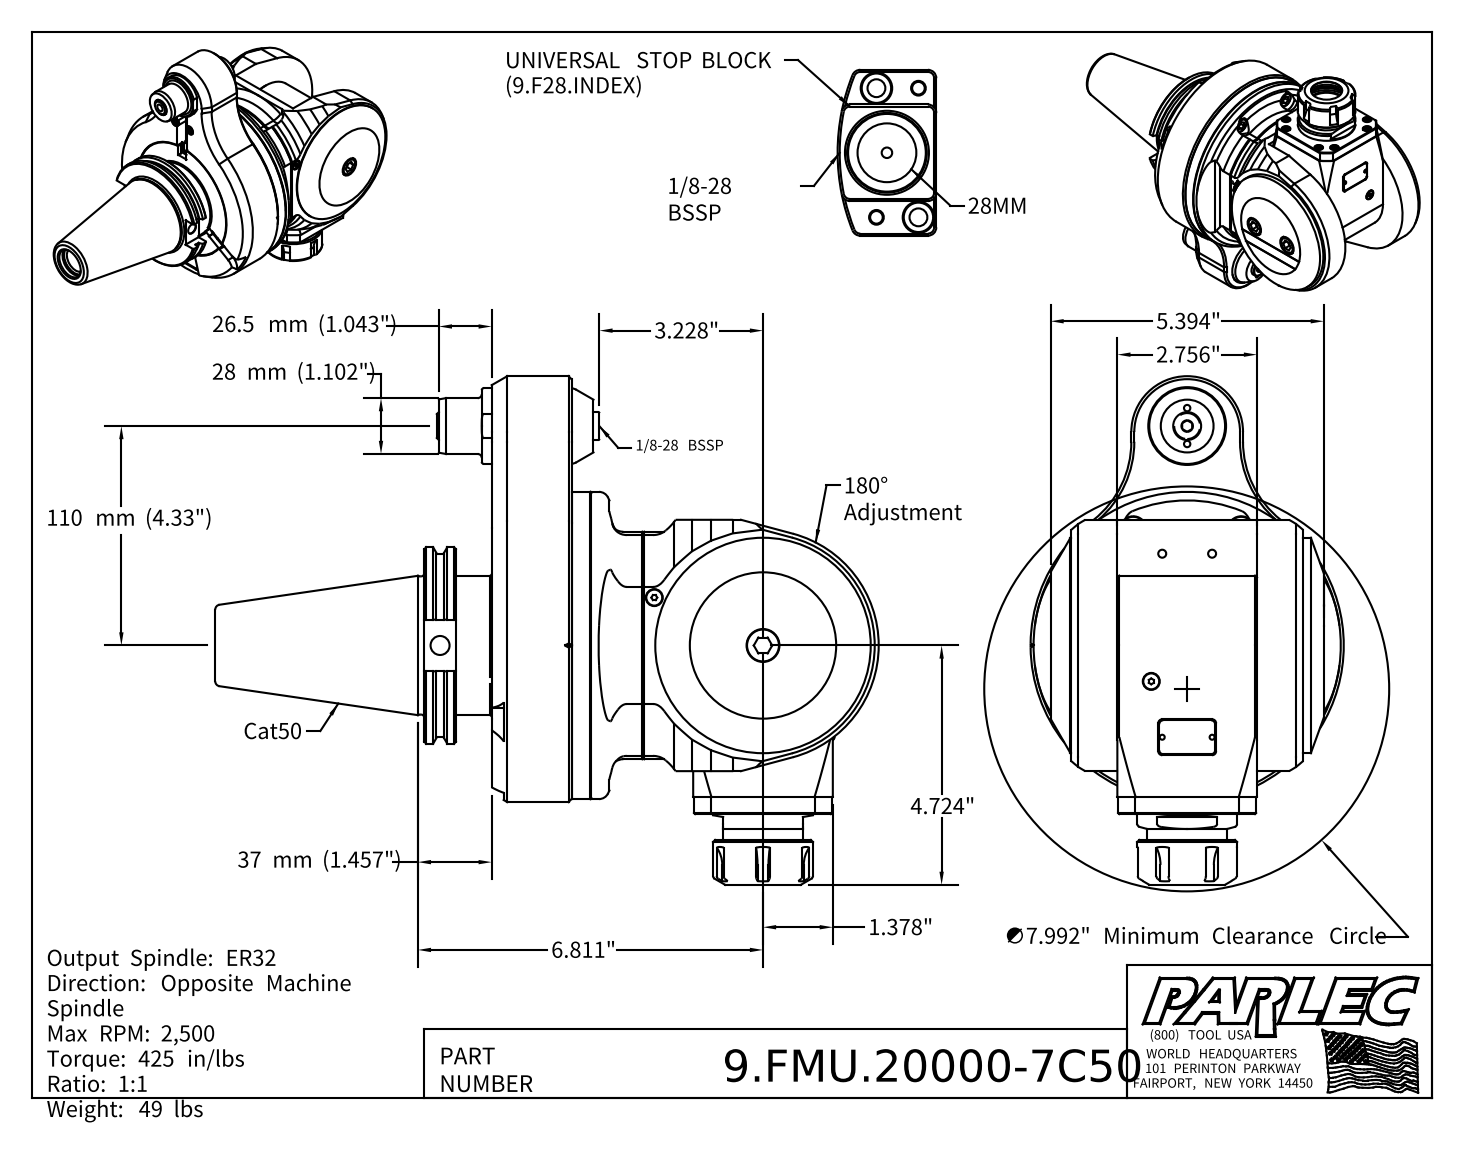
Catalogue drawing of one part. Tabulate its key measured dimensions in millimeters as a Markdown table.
| quantity | value |
| --- | --- |
| part name | 9.FMU.20000-7C50; 9_GA3_451_2 (Type 3, Cat50, 110mm); 9_FMU_20000 |
| STEP written by | Autodesk Inventor 2022 (AUTOMOTIVE_DESIGN) |
| units | millimeters |
| bodies | 5 solids, 891 faces (427 planar, 227 cylindrical, 237 other) |
| overall size | 332.6 × 255 × 157 |
| volume | 3 312 000 mm³ |
| surface area | 391 900 mm² |
| round holes (diameter × count) | 7.5 × 8, 6.8 × 4, 8.4 × 4, 13.5 × 4, 4.2 × 3, 16.5 × 3, 3.2 × 2, 4 × 2, 5.3 × 2, 8 × 2, 8.5 × 2, 2.5 × 1 |
| round bosses / shafts (diameter × count) | 7 × 8, 8 × 6, 13 × 4, 16 × 3, 28 × 2, 2.5 × 2, 154 × 1, 144 × 1 |
| partial cylindrical surfaces (radius × count) | 2 × 8, 15 × 7, 3 × 6, 7 × 6, 1 × 4, 5 × 4, 10 × 4, 2.5 × 2 |
| main face-to-face distances | 23, 70, 20.5, 35, 5, 93, 90.5, 113.5, 30, 6 |
| hole center spacings | 50.6, 64, 35.7, 59.3, 90.5, 108, 125, 35.7 |
